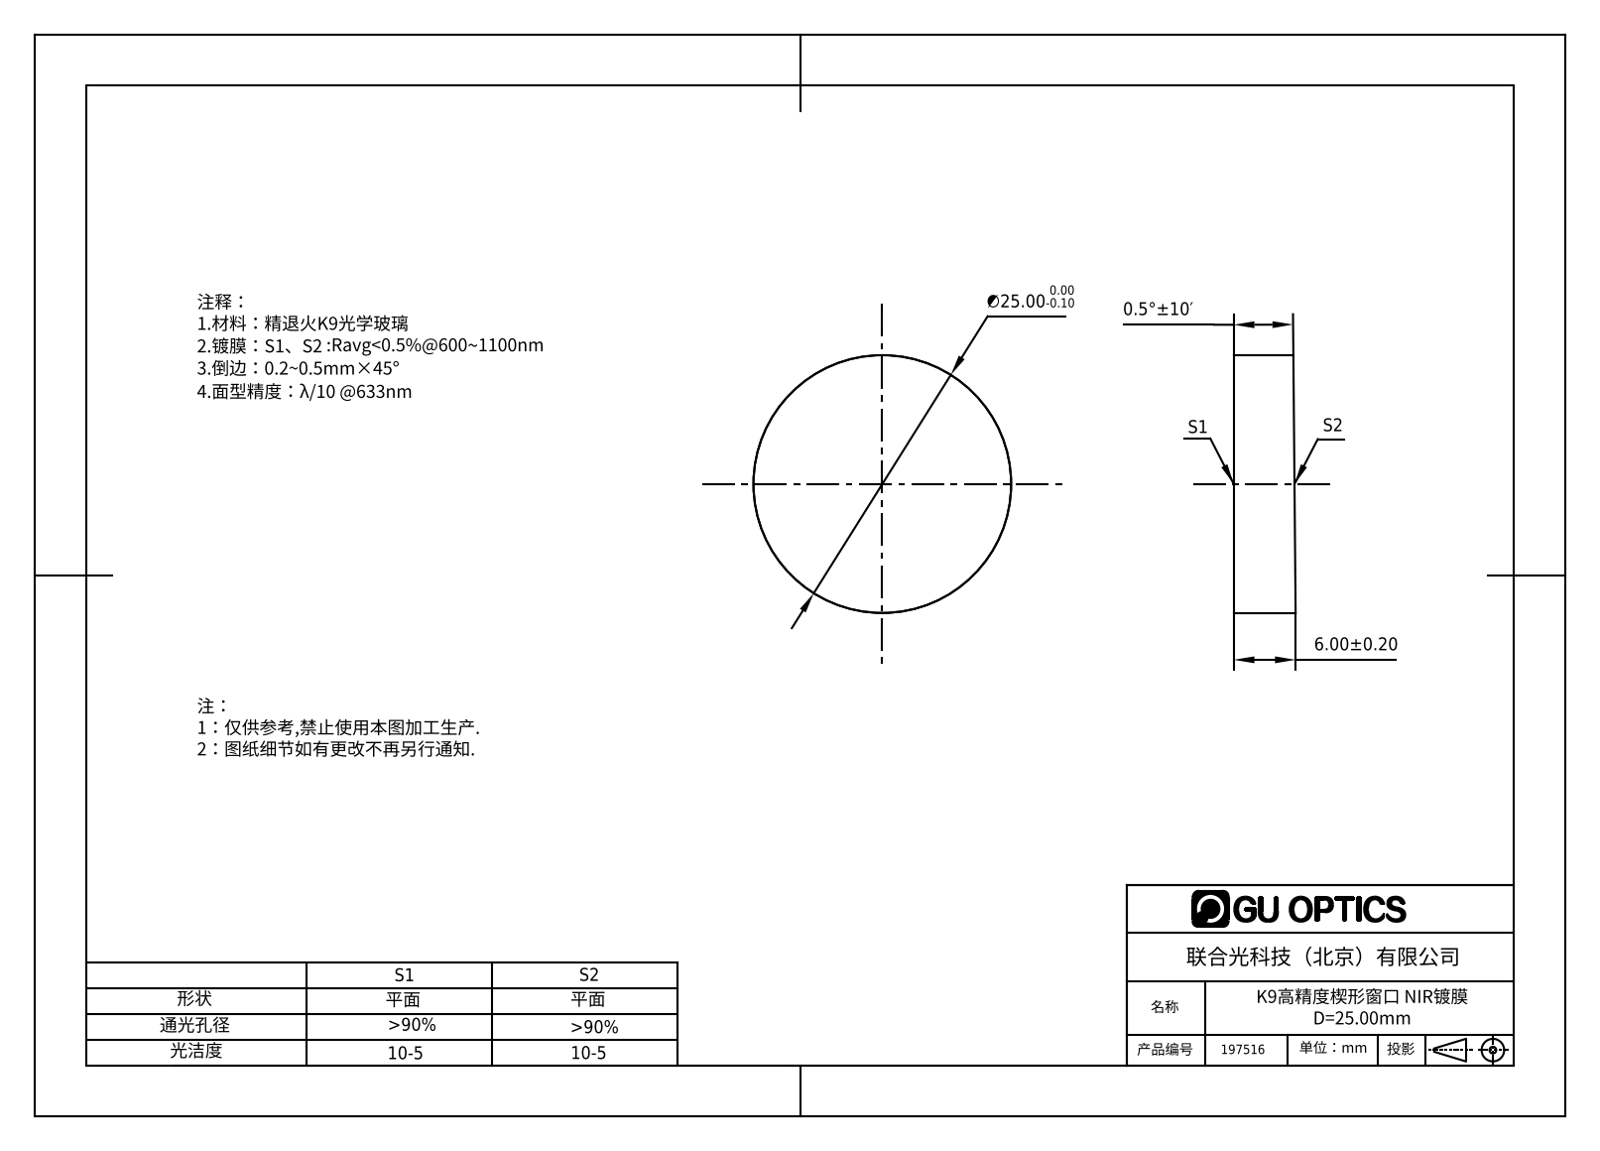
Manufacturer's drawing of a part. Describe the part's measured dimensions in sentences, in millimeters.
The part is named "197502". Its 3-D file was written by "SolidWorks 2016 (AUTOMOTIVE_DESIGN)". It is 1 solid with 4 faces: 2 planar, 2 cylindrical and 0 other. Overall it measures 25 by 25 by 6 millimeters. Its volume is 2 892 cubic millimeters and its surface area 1 445 square millimeters. Round bosses or shafts: 1 of diameter 25.
